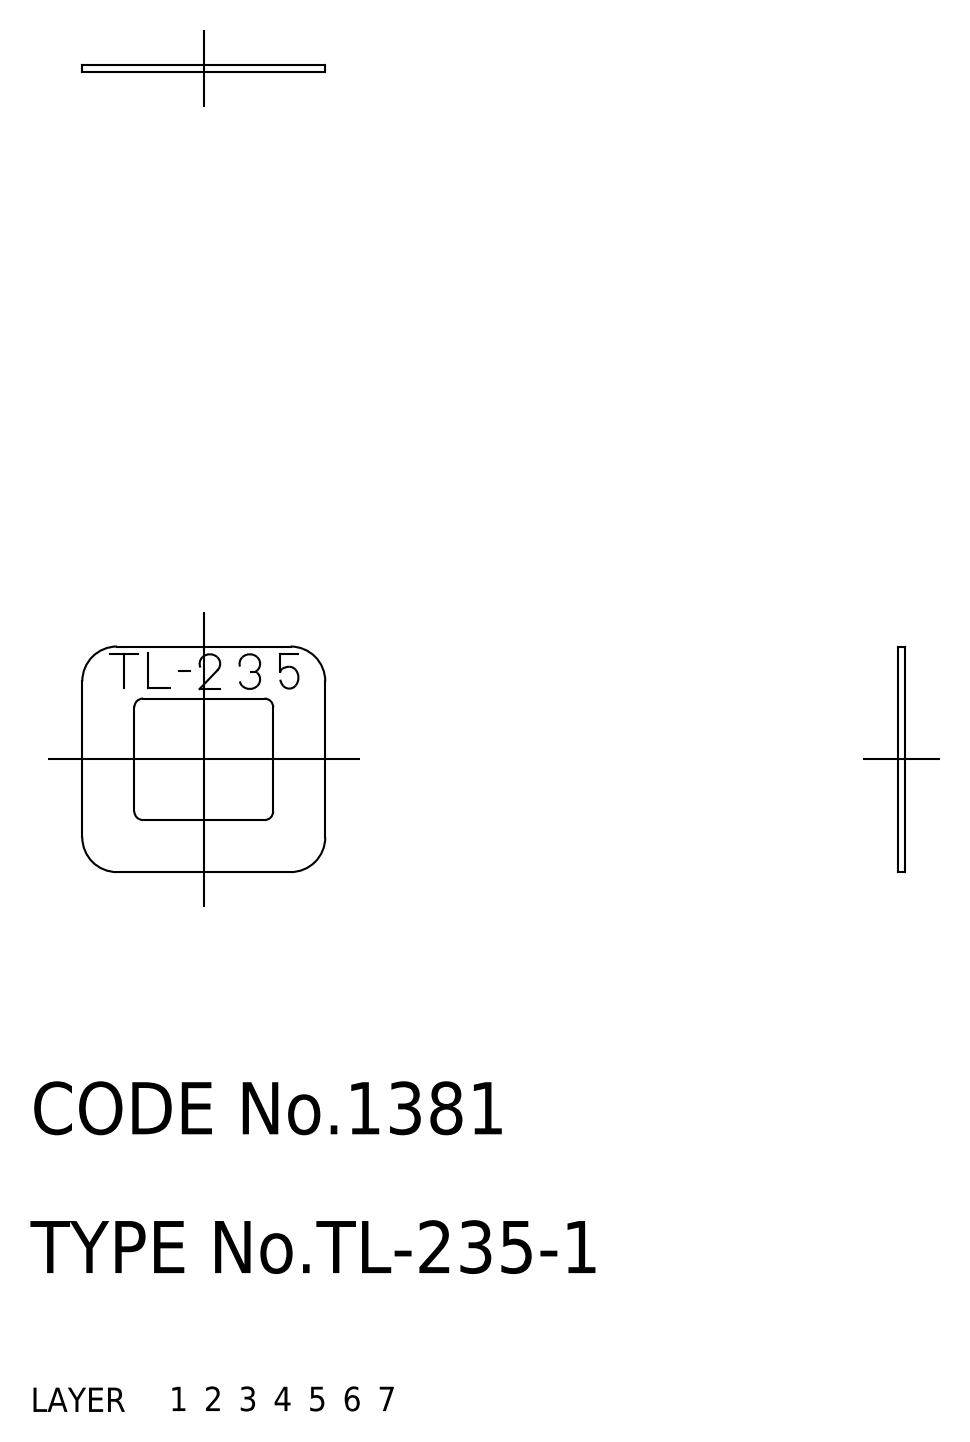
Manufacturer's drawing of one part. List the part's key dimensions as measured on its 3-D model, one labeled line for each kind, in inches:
Part name (STEP PRODUCT): spacer
STEP written by: CADfix (AUTOMOTIVE_DESIGN)
Units: inches
Bodies: 1 solid, 18 faces (0 planar, 0 cylindrical, 18 other)
Overall size (bounding box): 0.551 × 0.512 × 0.016
Volume: 0.003 in³ · Surface area: 0.429 in²
